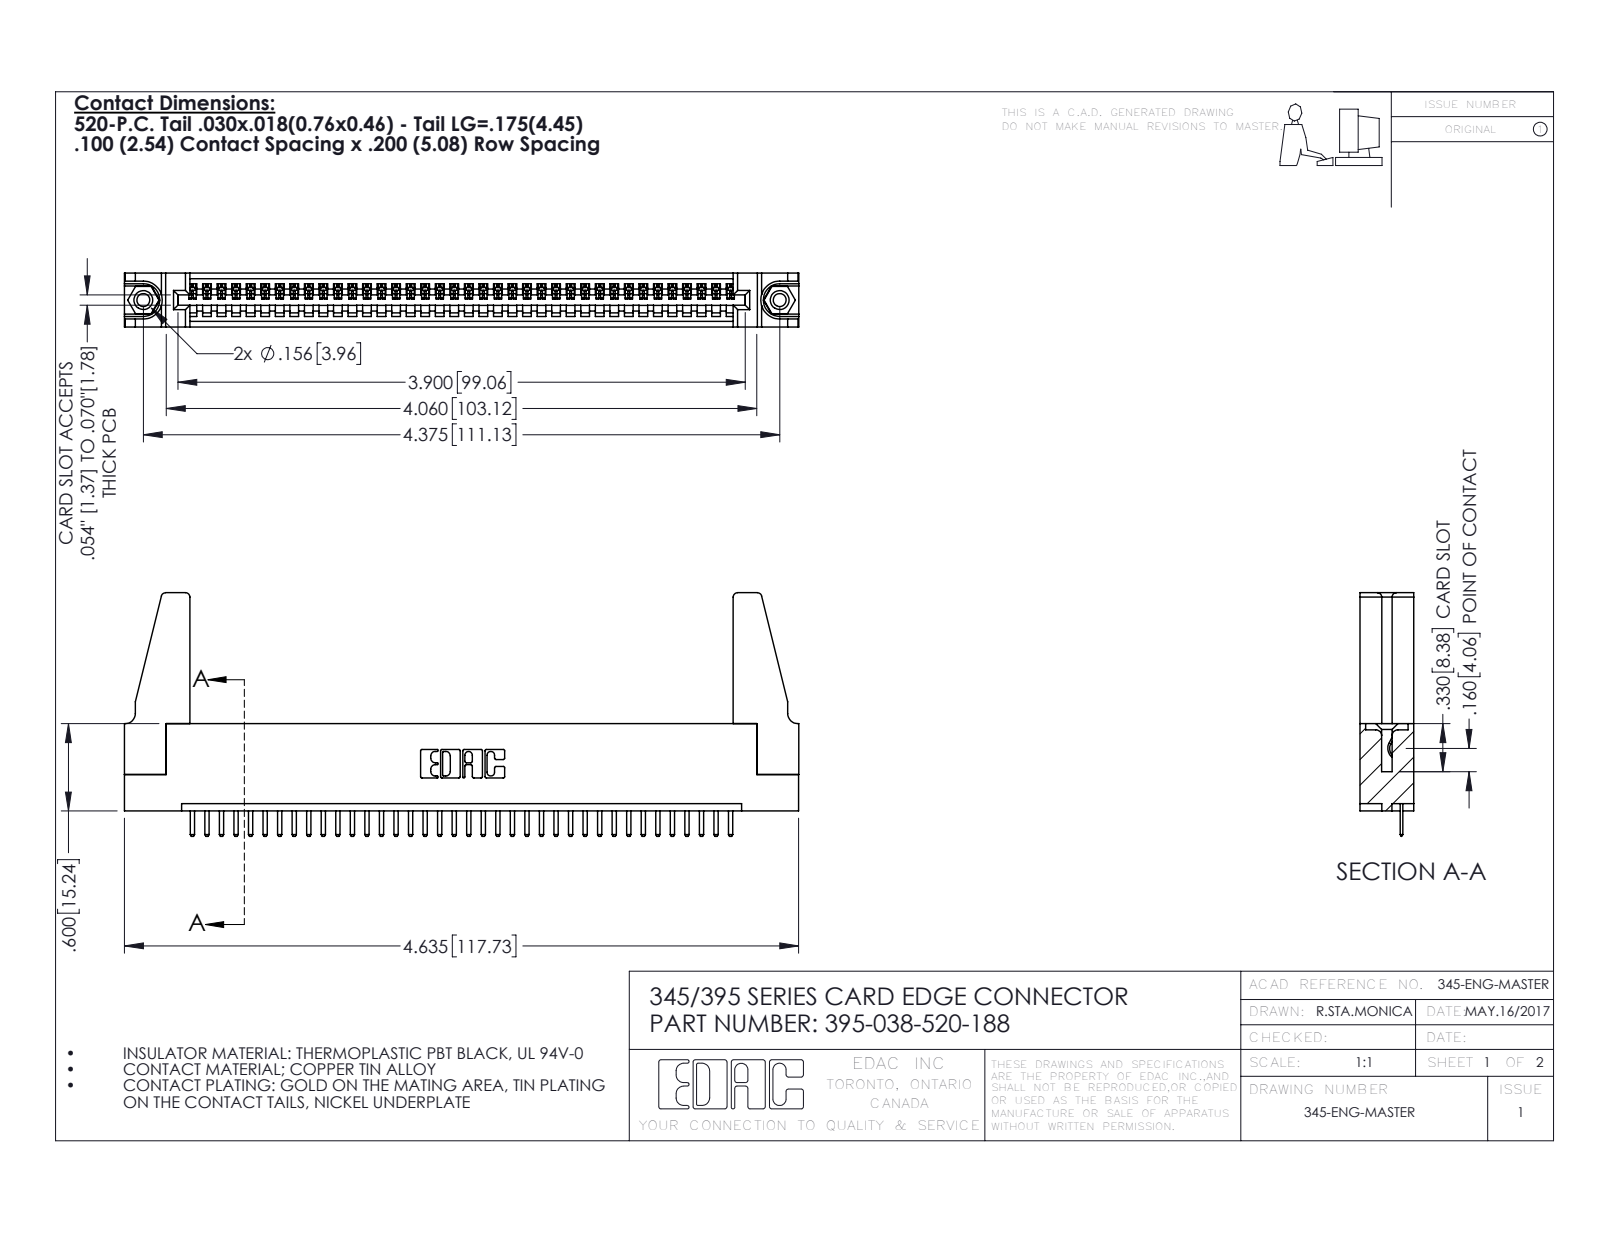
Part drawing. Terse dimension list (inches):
name: 345-250-001_345-250-001-102; 345-292-001_345-293-120; 395-038-520-188; 345-220-078_345-220-088 (+1 more)
written by: SolidWorks 2016 (CONFIG_CONTROL_DESIGN)
unit: in
bodies: 43 solids, 2606 faces (1748 planar, 842 cylindrical, 16 other)
size: 4.636 × 1.675 × 0.37
volume: 0.872 in³; area: 26.96 in²
holes: 2× ⌀0.089, 2× ⌀0.125, 2× ⌀0.156, 1× ⌀0.064
bosses: 2× ⌀0.155
rounds: 78× R0.01, 76× R0.006, 22× R0.01, 8× R0.03, 6× R0.007, 6× R0.031, 3× R0.026, 2× R0.031
face distances: 0.072, 0.37, 0.298, 0.2, 0.098, 0.272, 0.025, 0.225, 0.072, 0.149
hole spacings: 0.27, 4.139, 4.375
